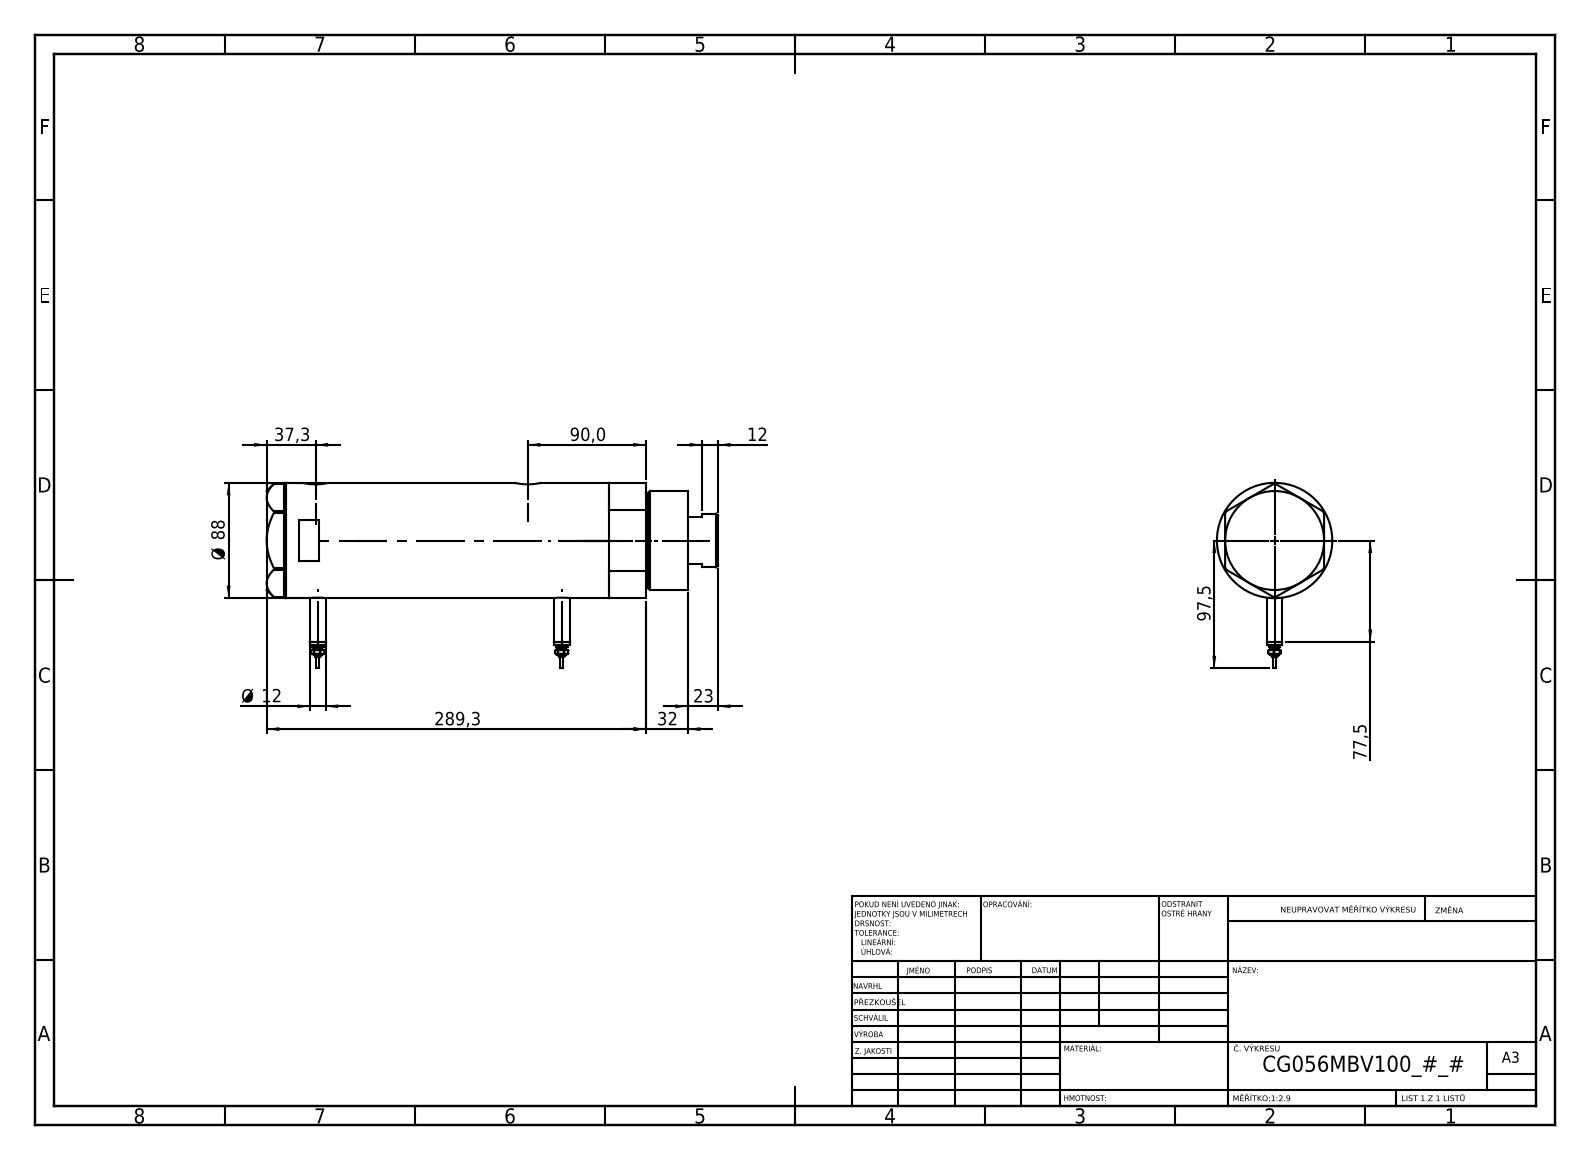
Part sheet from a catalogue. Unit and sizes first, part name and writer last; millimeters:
Units: millimetres
Overall size (bounding box): 344.3 × 141.5 × 88
Round holes (diameter × count): ⌀12.5 ×2, ⌀13.16 ×2, ⌀20 ×2, ⌀14.5 ×1, ⌀42 ×1, ⌀43.5 ×1, ⌀56 ×1, ⌀60 ×1, ⌀80 ×1
Round bosses / shafts (diameter × count): ⌀12 ×2, ⌀9 ×2, ⌀7 ×2, ⌀4.5 ×2, ⌀2.5 ×2, ⌀88 ×1, ⌀75 ×1, ⌀73 ×1
Main face-to-face distances: 184.4, 26, 158.4, 15, 41, 199.4, 306.3, 321.3, 280.3, 121.9
Hole centre spacings: 1.7, 25.8, 160.3, 162, 186.1, 187.8
Volume: 1 791 000 mm³ · Surface area: 253 806 mm²
Bodies: 6 solids, 213 faces (80 planar, 69 cylindrical, 64 other)
Part name (STEP PRODUCT): Switch; V270CG_BACK; V270CG_FRONT; V270CG_MIDDLE (+1 more)
STEP written by: SolidWorks 2019 (CONFIG_CONTROL_DESIGN)
